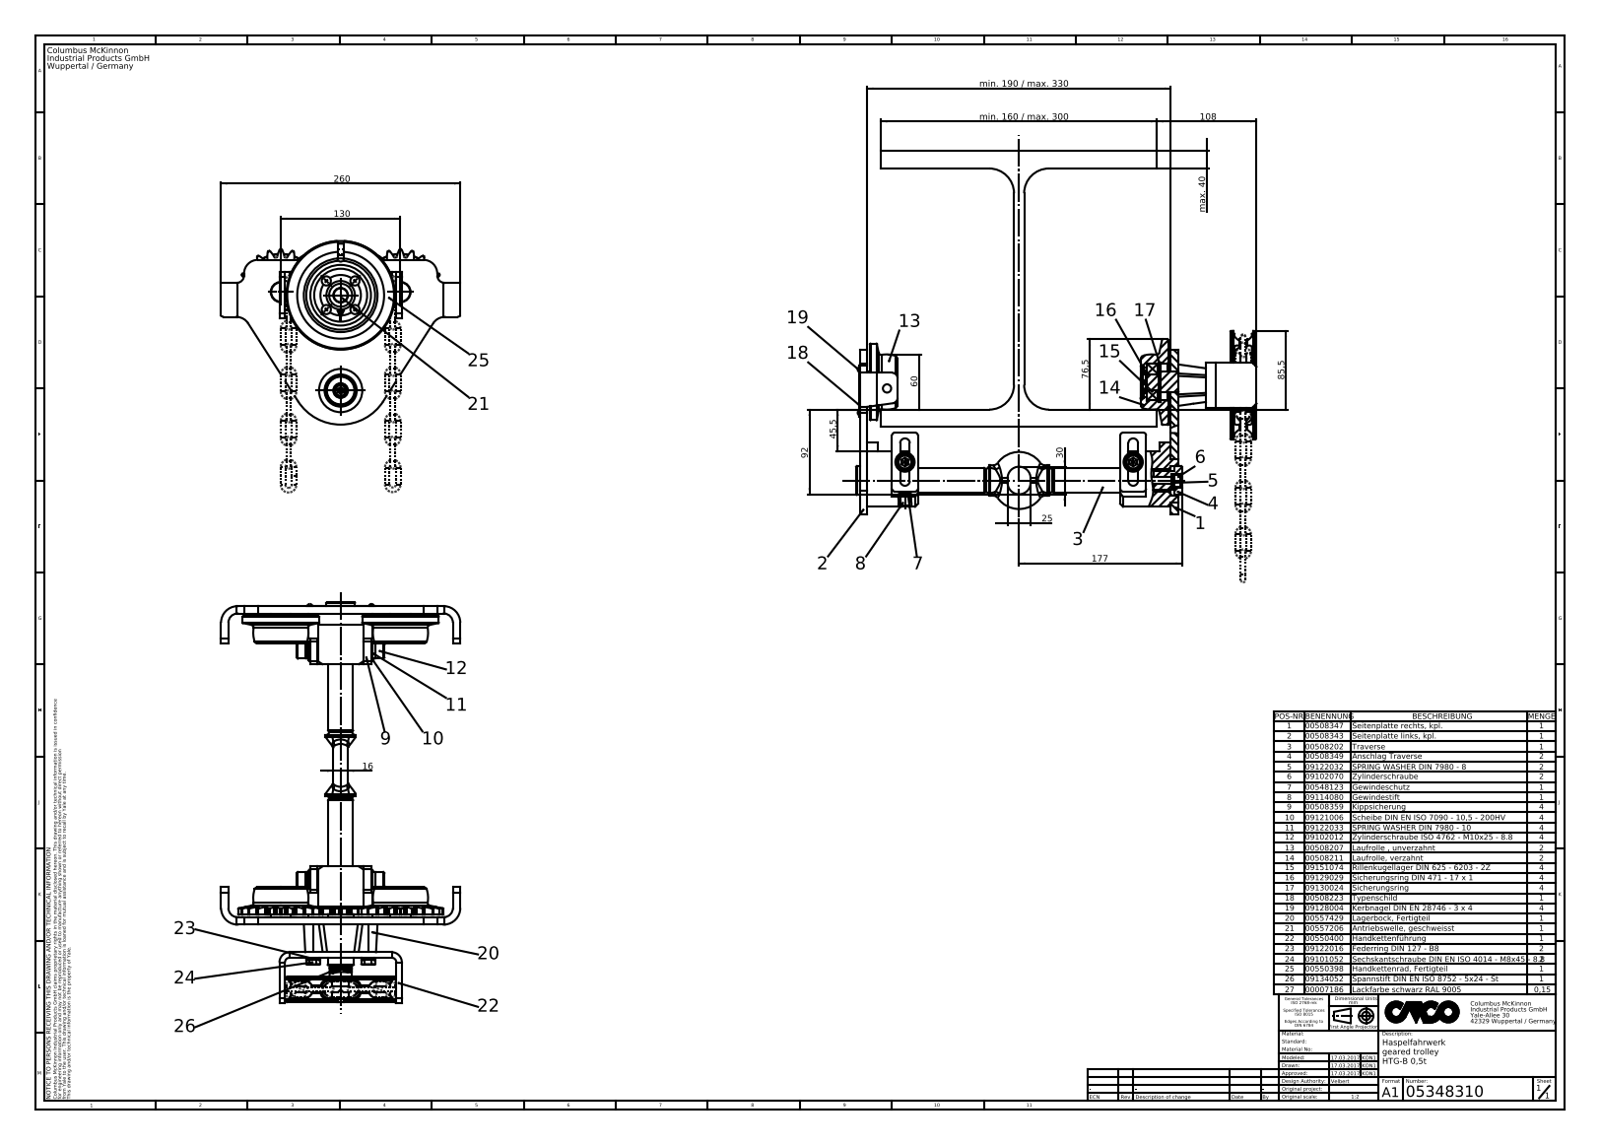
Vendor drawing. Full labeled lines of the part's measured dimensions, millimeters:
Part name (STEP PRODUCT): HTG-B 0,5t
STEP written by: SolidWorks 2015 (AUTOMOTIVE_DESIGN)
Units: millimetres
Bodies: 0 solids, 869 faces (274 planar, 368 cylindrical, 227 other)
Overall size (bounding box): 468.79 × 435 × 300
Round holes (diameter × count): ⌀10 ×4, ⌀32 ×3, ⌀1.7 ×2, ⌀9 ×2, ⌀22 ×2, ⌀34 ×2, ⌀35.7 ×2, ⌀4 ×1, ⌀6 ×1, ⌀15 ×1, ⌀16 ×1
Round bosses / shafts (diameter × count): ⌀5 ×20, ⌀83 ×2, ⌀23.79 ×2, ⌀21 ×2, ⌀17 ×2, ⌀16 ×2, ⌀14.1 ×2, ⌀118 ×1
Partial cylindrical surfaces — rounded edges, fillets, slot ends (radius × count): R20 ×58, R1 ×44, R10 ×18, R1.5 ×13, R3 ×6, R5.25 ×4, R6 ×4, R8 ×4
Main face-to-face distances: 19, 281, 300, 11, 167.5, 262, 8, 178.5, 159.5, 170.5
Hole centre spacings: 22.01, 31.12, 9.99, 21.23, 44.01, 48.14, 50.91, 52.96
